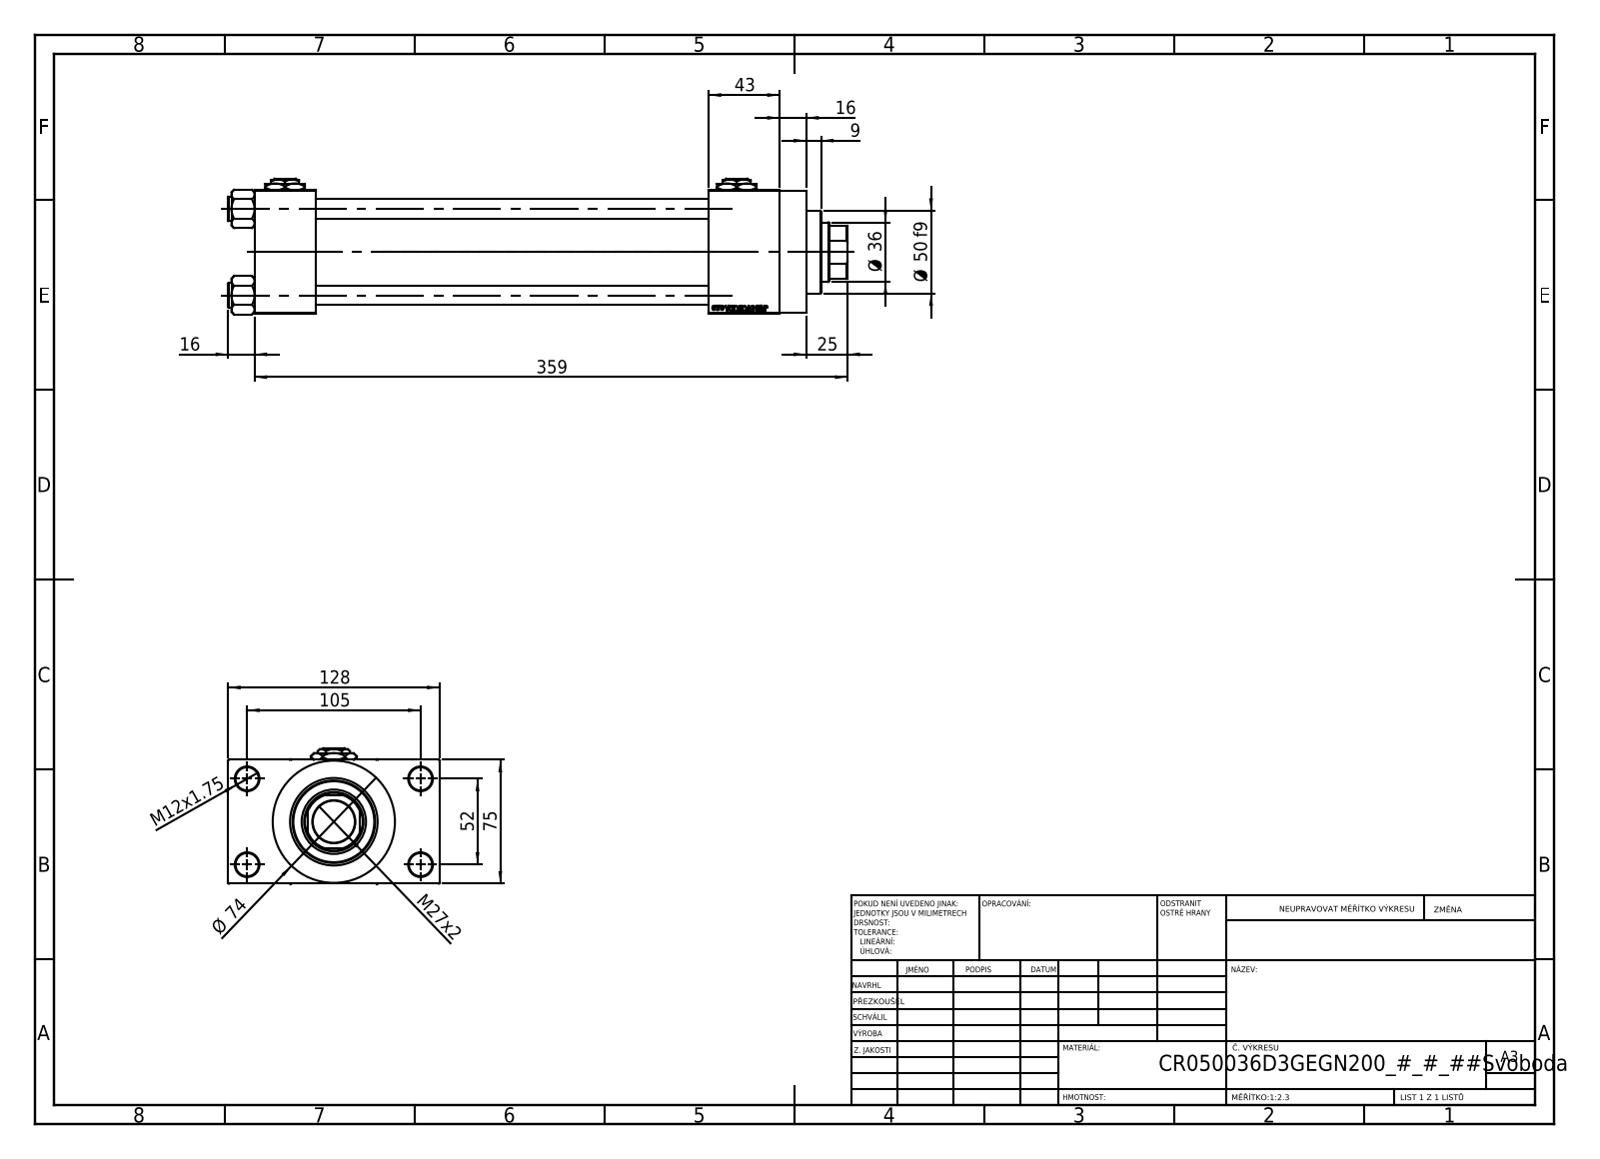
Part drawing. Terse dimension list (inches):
name: V215_VC_A; V215CR_D_Body; Zatka_pro_OIL_PORT; NUT_M5_D (+2 more)
written by: SolidWorks 2019 (CONFIG_CONTROL_DESIGN)
unit: in
bodies: 13 solids, 1205 faces (545 planar, 100 cylindrical, 560 other)
size: 14.764 × 5.039 × 3.239
volume: 71.82 in³; area: 442.5 in²
holes: 4× ⌀0.472, 4× ⌀0.551, 2× ⌀0.276, 2× ⌀0.825, 2× ⌀1.181, 1× ⌀1.004, 1× ⌀1.417, 1× ⌀1.535, 1× ⌀1.614, 1× ⌀2.087
bosses: 4× ⌀0.591, 1× ⌀2.913, 1× ⌀2.205, 1× ⌀1.969
rounds: 1× R0.689
face distances: 2.953, 9.37, 1.457, 10.827, 1.043, 3.996, 12.52, 1.693, 11.063, 0.63
hole spacings: 1.037, 1.456, 2.059, 2.3, 2.307, 3.096, 3.715, 2.047
